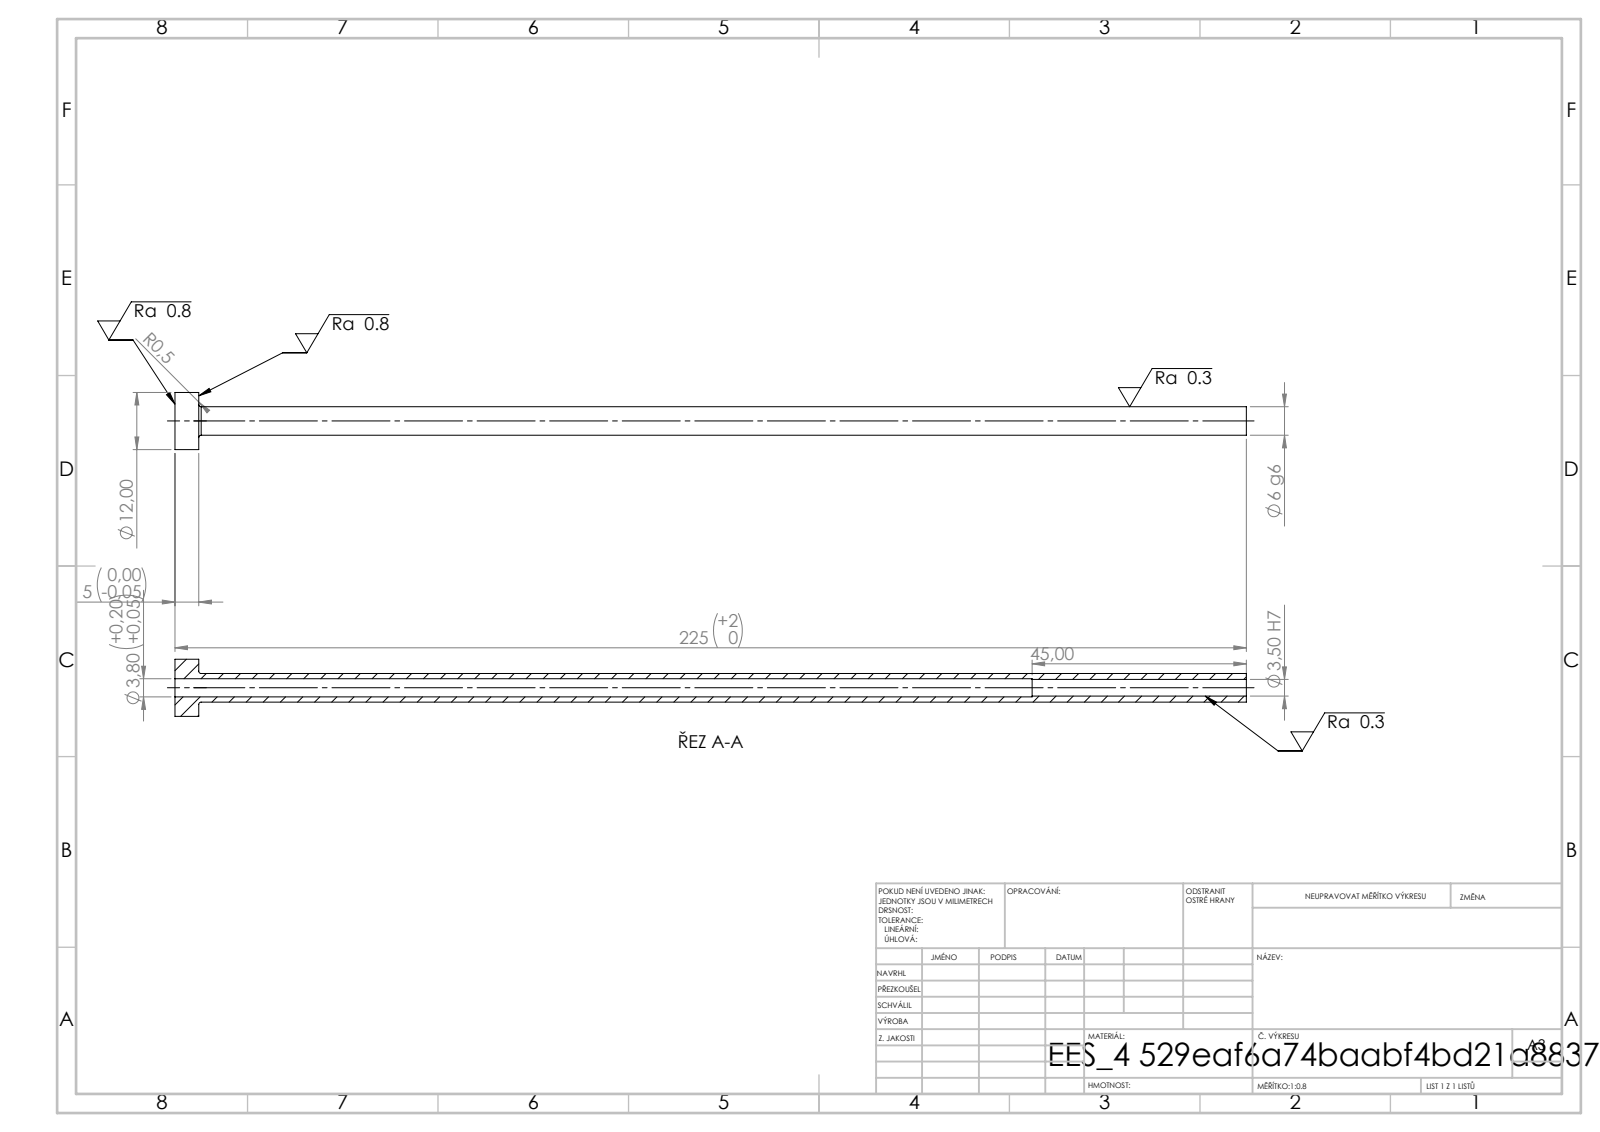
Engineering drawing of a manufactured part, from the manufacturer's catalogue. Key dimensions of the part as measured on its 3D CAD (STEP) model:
STEP written by: SolidWorks 2019 (CONFIG_CONTROL_DESIGN)
Units: millimetres
Bodies: 1 solid, 14 faces (4 planar, 8 cylindrical, 2 other)
Overall size (bounding box): 225 × 12 × 12
Volume: 4 313 mm³ · Surface area: 7 182 mm²
Round holes (diameter × count): ⌀3.5 ×1, ⌀3.8 ×1
Round bosses / shafts (diameter × count): ⌀12 ×1, ⌀6 ×1
Main face-to-face distances: 5, 225, 220, 180, 175, 45
